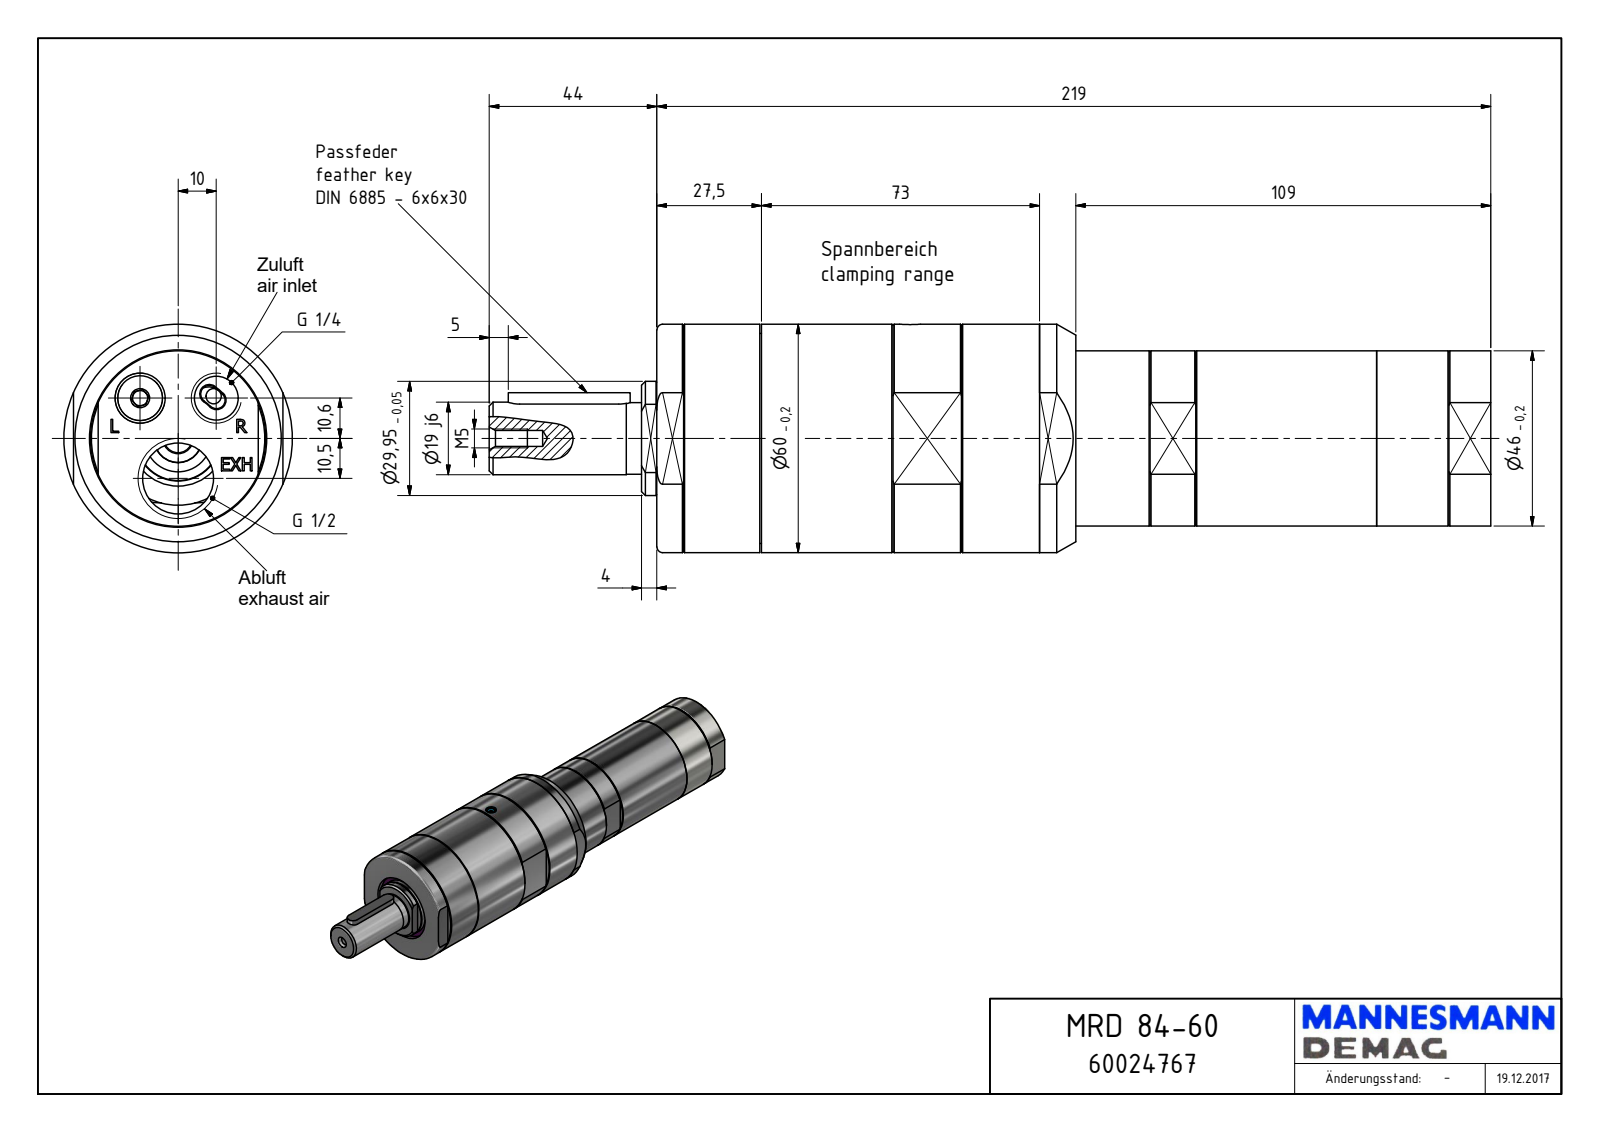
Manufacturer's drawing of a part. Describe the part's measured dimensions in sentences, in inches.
The part is named "MRD 84-60_60024767". Its 3-D file was written by "Autodesk Inventor 2018 (AUTOMOTIVE_DESIGN)". It is 1 solid with 239 faces: 133 planar, 55 cylindrical and 51 other. Overall it measures 10.354 by 2.362 by 2.362 inches. Its volume is 30.26 cubic inches and its surface area 81.82 square inches. Round holes: 2 of diameter 0.157, 1 of diameter 0.061, 1 of diameter 0.163, 1 of diameter 0.217, 1 of diameter 0.451, 1 of diameter 0.733, 1 of diameter 1.378, 1 of diameter 1.831, 1 of diameter 2.18, 1 of diameter 2.244. Round bosses or shafts: 1 of diameter 2.362, 1 of diameter 2.172, 1 of diameter 2.125, 1 of diameter 1.811, 1 of diameter 1.621, 1 of diameter 1.575, 1 of diameter 1.311, 1 of diameter 0.748. Partial cylindrical surfaces (rounded edges, fillets, slot ends): 4 of radius 0.098, 2 of radius 0.118, 2 of radius 0.197, 1 of radius 0.225, 1 of radius 0.589, 1 of radius 0.659, 1 of radius 0.748. The main face-to-face distances are 0.256, 8.622, 2.165, 1.909, 0.02, 2.992, 4.331, 4.291, 4.055, 0.276. The hole center spacings are 0.574, 0.919, 0.413, 0.787.
